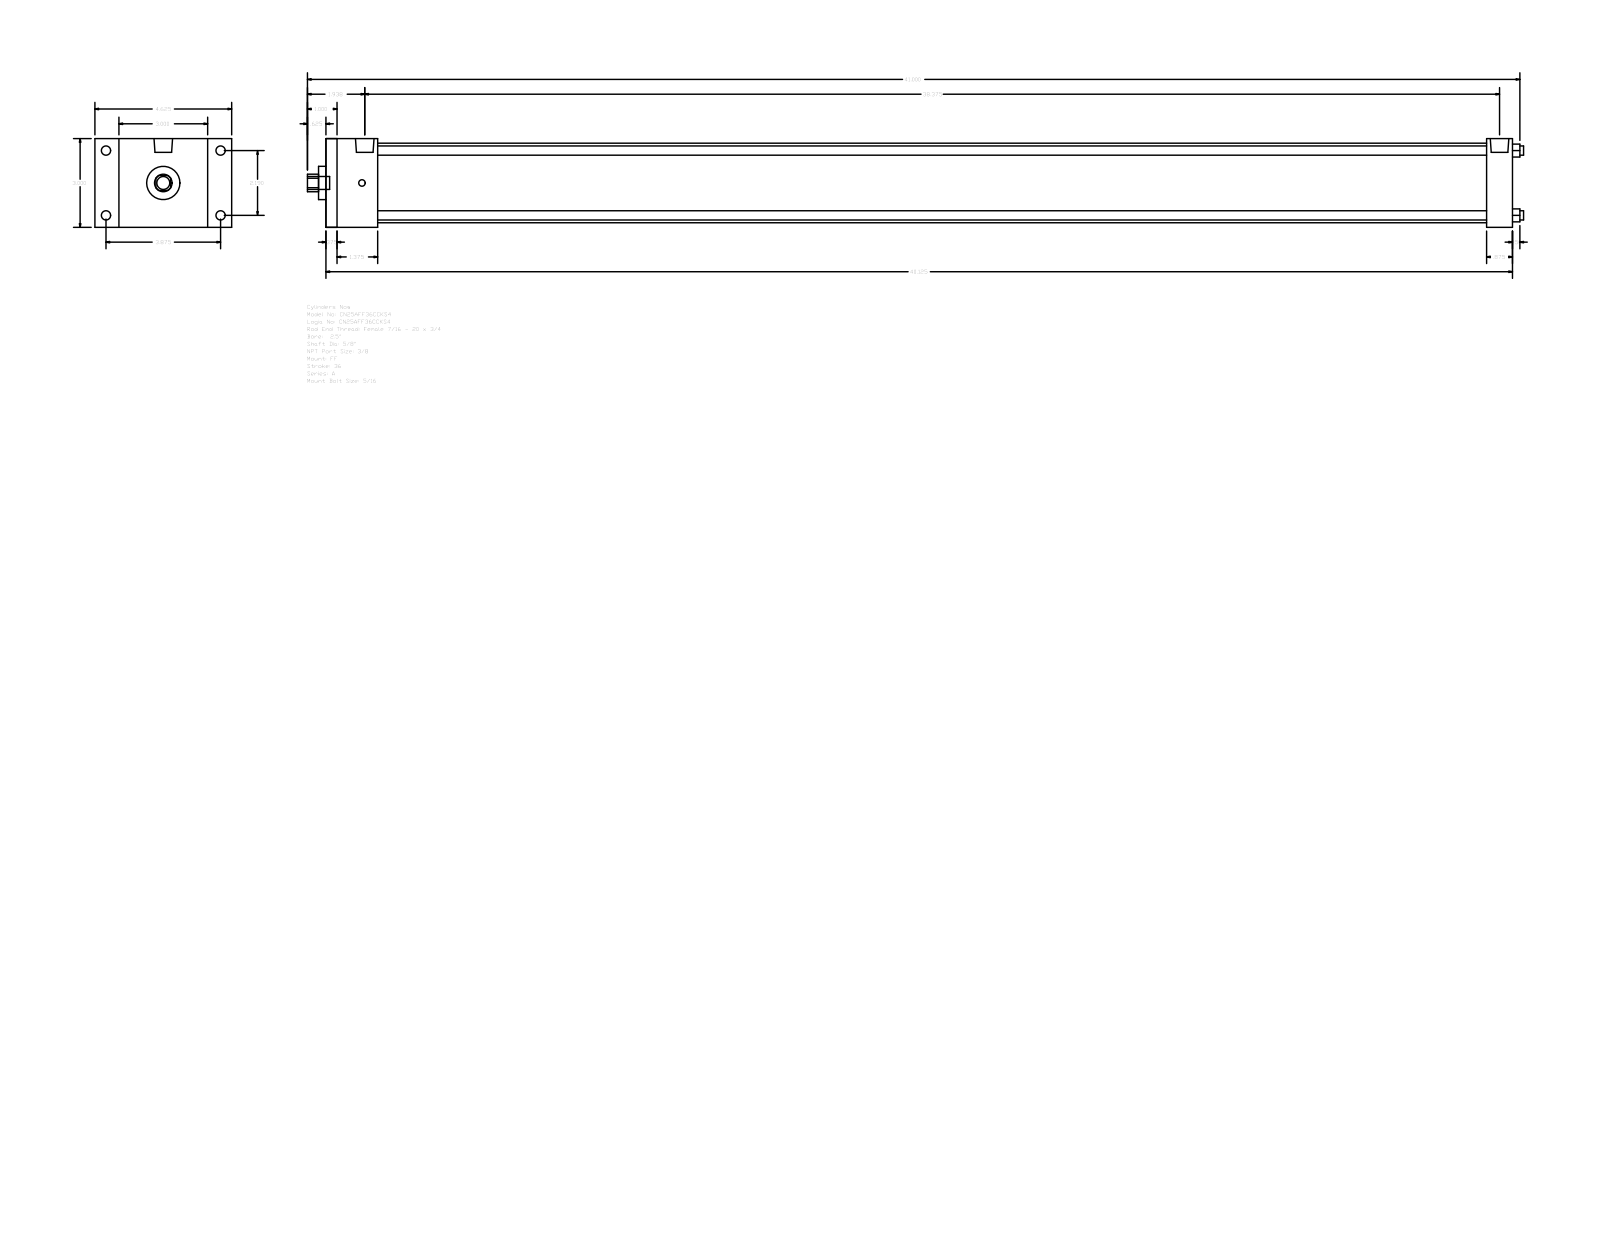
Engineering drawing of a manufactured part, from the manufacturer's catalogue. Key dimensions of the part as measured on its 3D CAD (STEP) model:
Part name (STEP PRODUCT): A_FF__0250_0.625
STEP written by: GSSL Pune (CONFIG_CONTROL_DESIGN)
Units: millimetres
Bodies: 0 solids, 92 faces (64 planar, 28 cylindrical, 0 other)
Overall size (bounding box): 1044.58 × 117.47 × 76.2
Round holes (diameter × count): ⌀7.94 ×4, ⌀15.88 ×1, ⌀28.57 ×1, ⌀68.33 ×1
Round bosses / shafts (diameter × count): ⌀7.94 ×4, ⌀5.56 ×4, ⌀15.93 ×2, ⌀11.11 ×1
Partial cylindrical surfaces — rounded edges, fillets, slot ends (radius × count): R7.54 ×1
Main face-to-face distances: 76.2, 1019.17, 9.52, 1009.65, 44.45, 996.95, 34.93, 987.43, 952.5, 974.72
Hole centre spacings: 39.33, 55.62, 78.66
